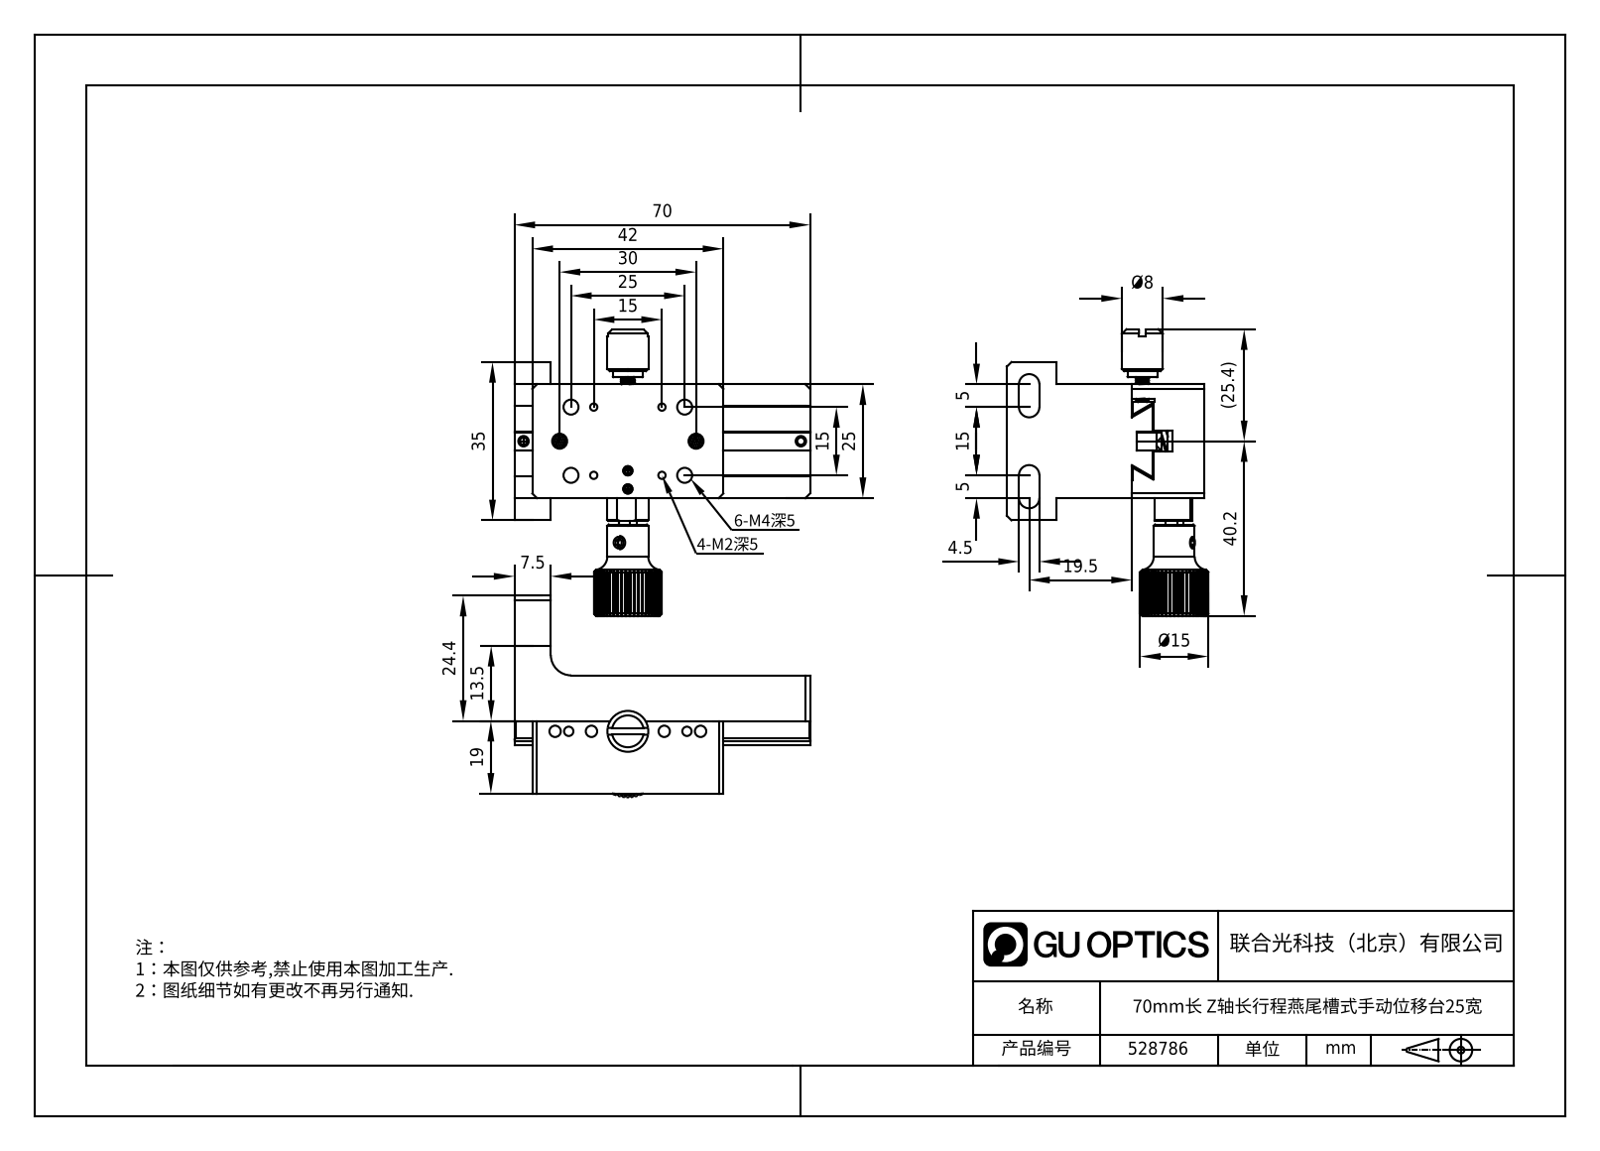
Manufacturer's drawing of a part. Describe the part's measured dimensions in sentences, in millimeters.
The part is named "528786". Its 3-D file was written by "SolidWorks 2020 (CONFIG_CONTROL_DESIGN)". It is 11 solids with 894 faces: 548 planar, 119 cylindrical and 227 other. Overall it measures 70 by 63.01 by 44.03 millimeters. Its volume is 41 558 cubic millimeters and its surface area 19 836 square millimeters. Round holes: 6 of diameter 1.6, 6 of diameter 2.5, 6 of diameter 3.3, 4 of diameter 2.05, 2 of diameter 2.3, 1 of diameter 4, 1 of diameter 4.5, 1 of diameter 8. Round bosses or shafts: 2 of diameter 9, 2 of diameter 3.8, 2 of diameter 2.5, 2 of diameter 2, 1 of diameter 7, 1 of diameter 6.85, 1 of diameter 6.5, 1 of diameter 2.95. Partial cylindrical surfaces (rounded edges, fillets, slot ends): 8 of radius 0.2, 6 of radius 2.25, 2 of radius 4.5, 1 of radius 7.5. The main face-to-face distances are 14.5, 25, 4.5, 10, 10.5, 16, 26, 11.5, 4, 11.1. The hole center spacings are 5, 15, 25, 7.91, 8, 10.61, 15.81, 20.
